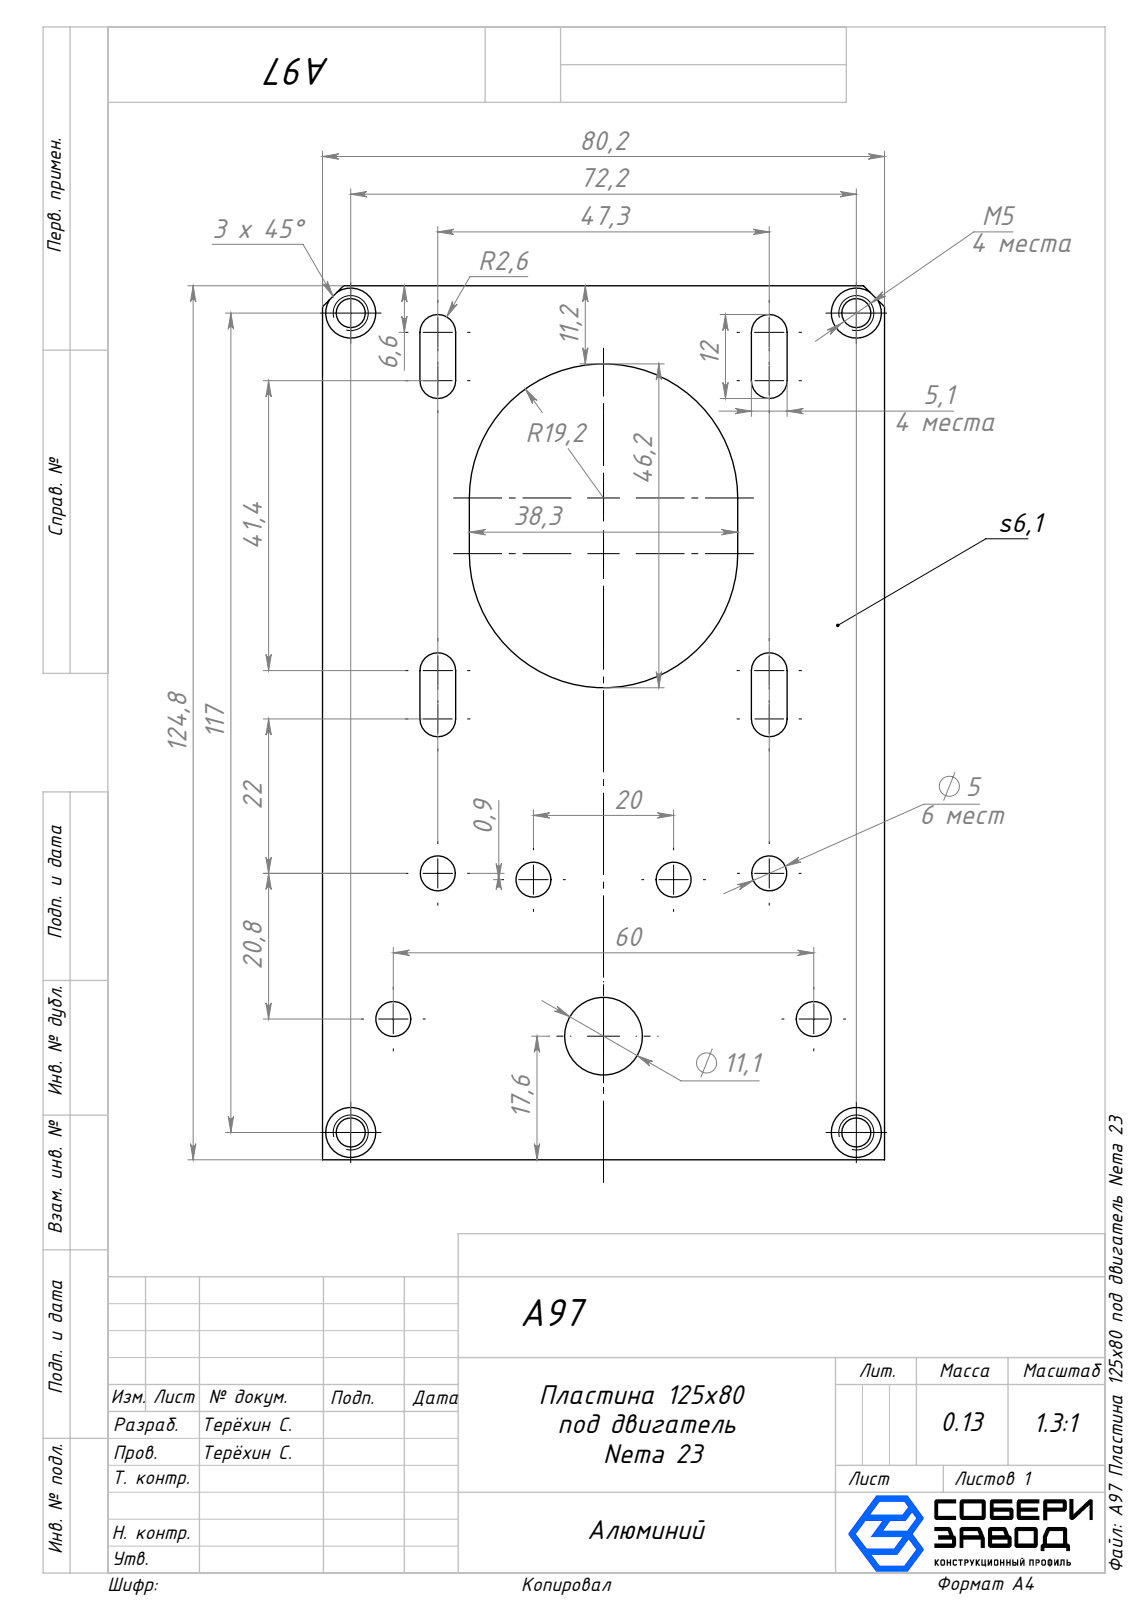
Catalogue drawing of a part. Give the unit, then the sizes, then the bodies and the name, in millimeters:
Units: millimetres
Overall size (bounding box): 124.8 × 80.2 × 6.1
Round holes (diameter × count): ⌀5 ×6, ⌀4.15 ×4, ⌀11.1 ×1
Partial cylindrical surfaces — rounded edges, fillets, slot ends (radius × count): R2.55 ×8, R19.15 ×2
Main face-to-face distances: 6.1, 80.2, 124.8, 19, 61.2, 13.9, 66.3, 5.1, 47.3, 20.95
Hole centre spacings: 13.68, 17.3, 21.75, 24.49, 28.21, 30.1, 33.16, 33.66
Volume: 49 046 mm³ · Surface area: 21 214 mm²
Bodies: 1 solid, 58 faces (18 planar, 32 cylindrical, 8 other)
Part name (STEP PRODUCT): A97 Пластина 125x80 под двигатель Nema 23; A97 Пластина 125x80 под двигатель Nema 23_00
STEP written by: SolidWorks 2026 (CONFIG_CONTROL_DESIGN)
